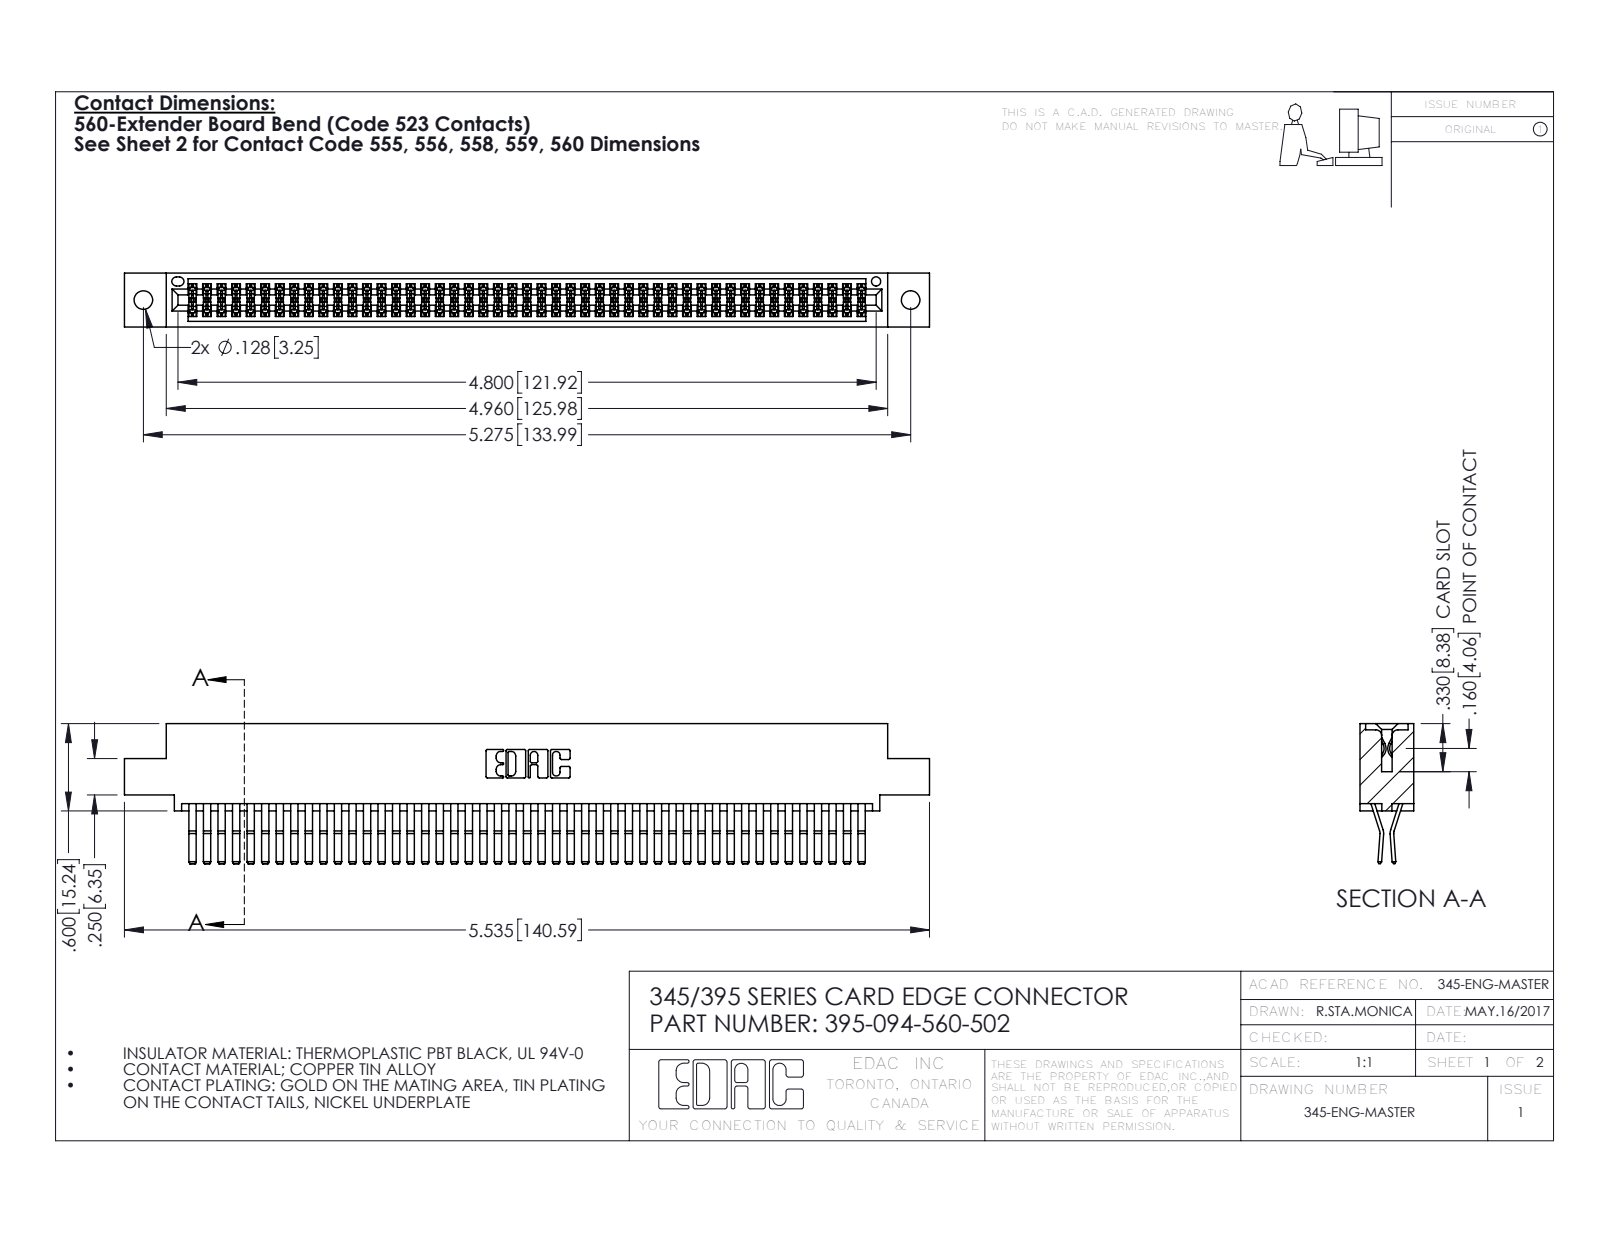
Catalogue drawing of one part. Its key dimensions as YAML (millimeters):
part_name: "345 Part_0.110 Offset - 0.128 Dia; 345-292-001_560 Tail; 395-094-560-502"
step_written_by: "SolidWorks 2016 (CONFIG_CONTROL_DESIGN)"
units: millimeters
bodies: {solids: 95, faces: 5018, planar: 3186, cylindrical: 1832, other: 0}
overall_size: [140.6, 24.4, 9.4]
volume: 14200
surface_area: 22500
round_holes:
  - {diameter: 3.3, count: 2}
  - {diameter: 1.6, count: 1}
partial_cylinders:
  - {radius: 0.2, count: 141}
  - {radius: 0.3, count: 22}
  - {radius: 0.2, count: 6}
  - {radius: 0.8, count: 6}
  - {radius: 0.7, count: 3}
  - {radius: 0.3, count: 2}
  - {radius: 0.4, count: 2}
  - {radius: 0.5, count: 2}
face_to_face_distances: [0.6, 7.6, 1.8, 9.4, 5.1, 2.5, 6.9, 5.7, 4.4, 3.8]
hole_center_spacings: [6.9, 128, 134]
